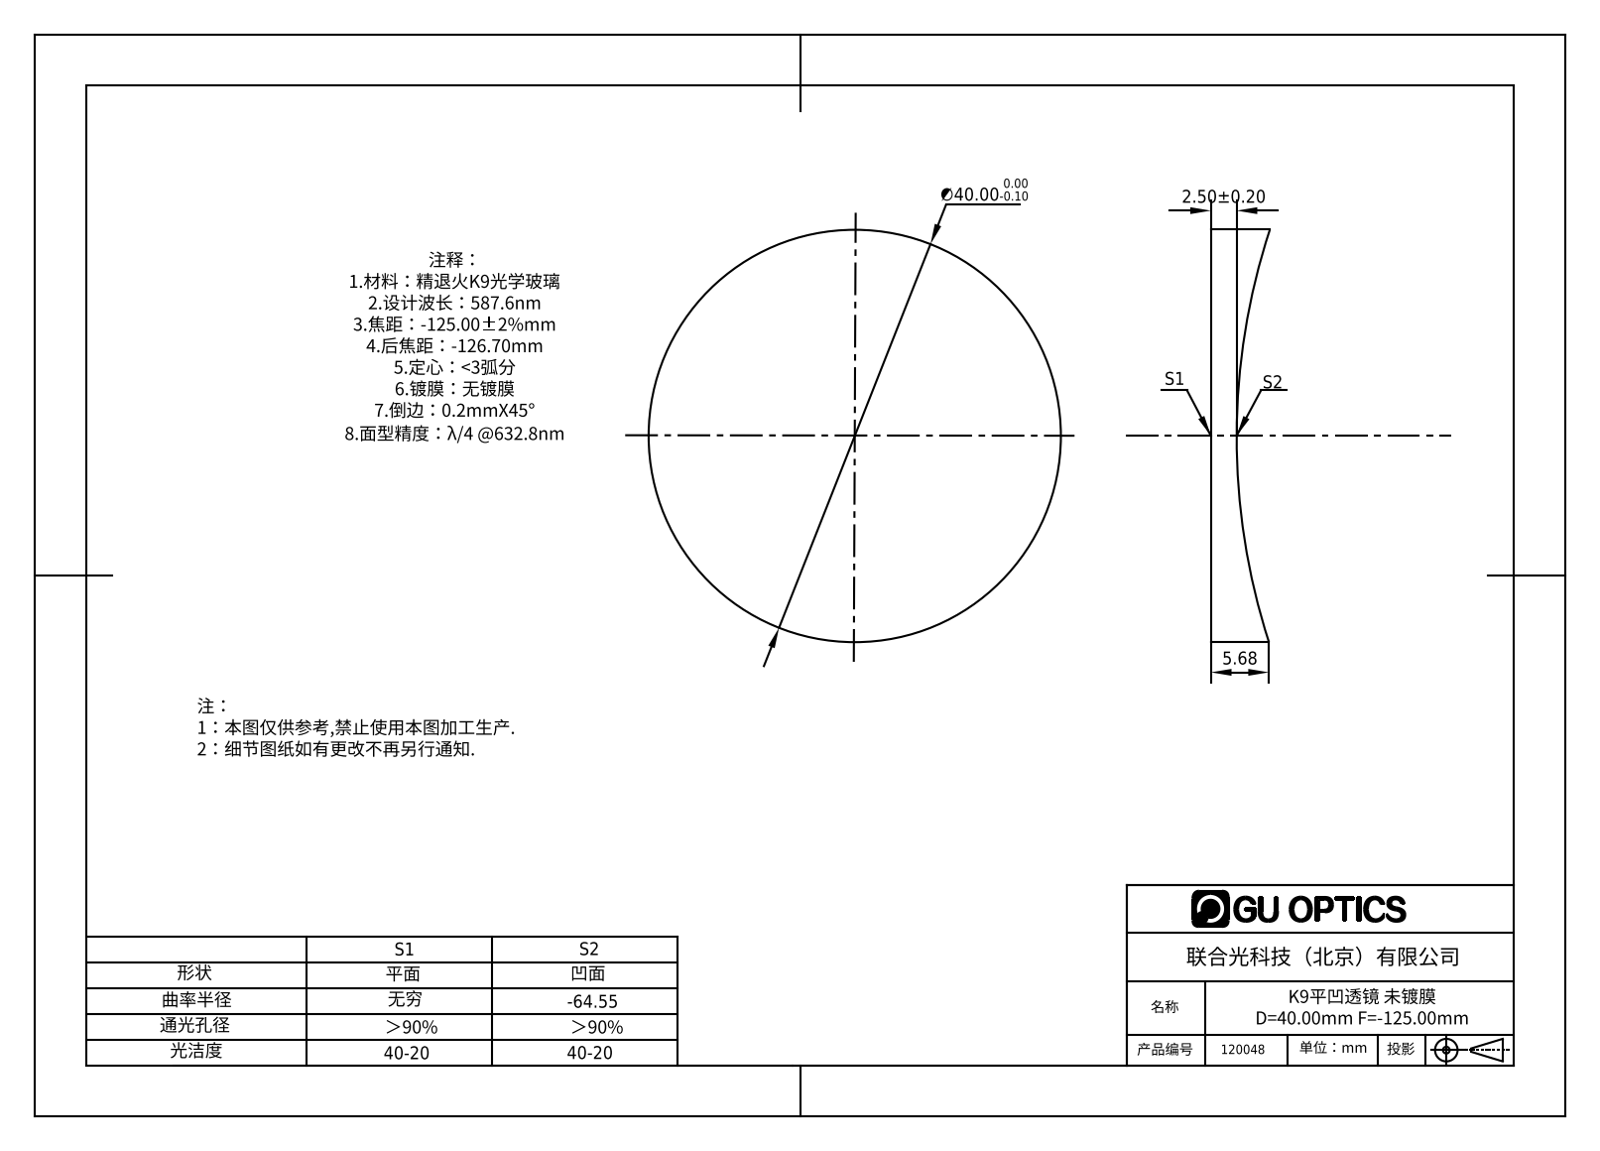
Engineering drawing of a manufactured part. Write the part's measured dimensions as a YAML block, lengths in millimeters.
part_name: "120048"
step_written_by: "SolidWorks 2016 (AUTOMOTIVE_DESIGN)"
units: millimeters
bodies: {solids: 1, faces: 5, planar: 1, cylindrical: 2, other: 2}
overall_size: [40, 40, 5.73]
volume: 5161
surface_area: 3265
round_bosses_or_shafts:
  - {diameter: 40, count: 1}
